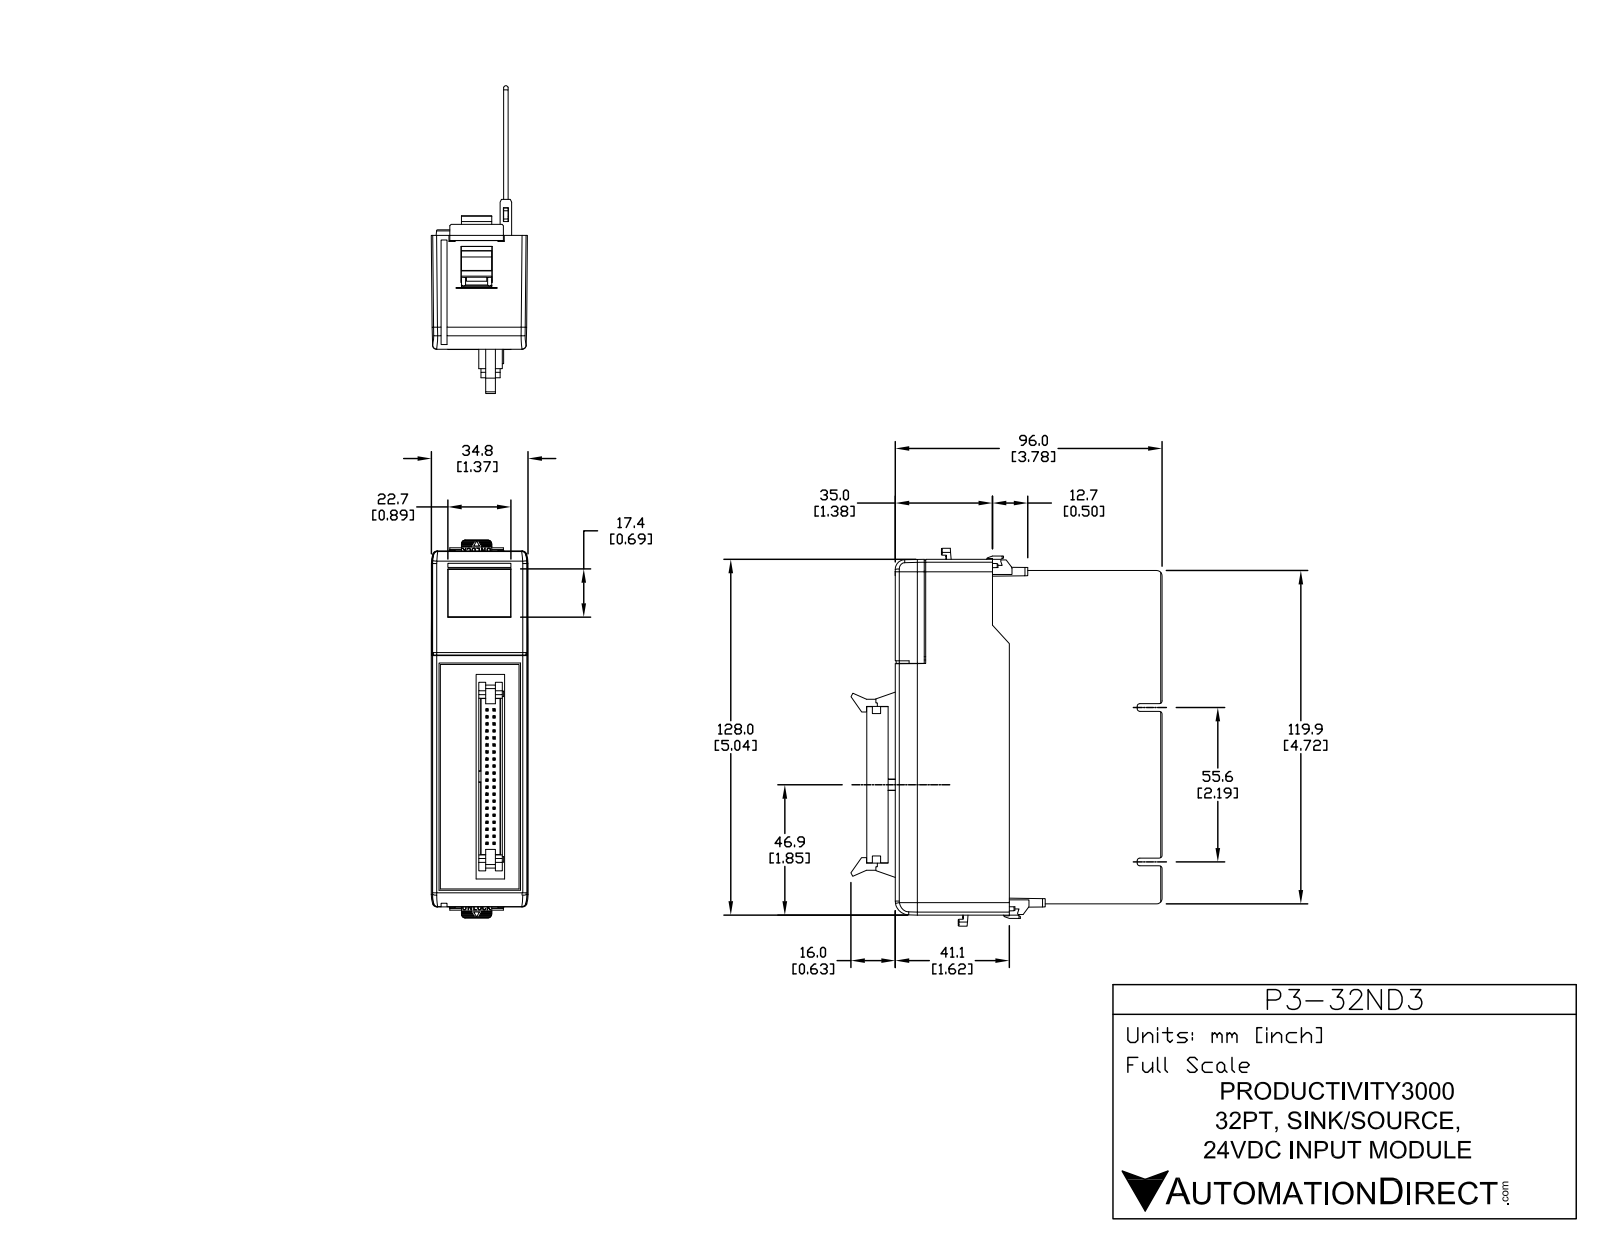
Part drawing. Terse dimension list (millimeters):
name: P3-32ND3
written by: SolidWorks 2009 (CONFIG_CONTROL_DESIGN)
unit: mm
bodies: 1 solid, 1418 faces (1334 planar, 54 cylindrical, 30 other)
size: 136.08 × 111.89 × 34.8
volume: 190 469 mm³; area: 44 248 mm²
rounds: 16× R1, 10× R0.3, 6× R1.5, 2× R0.1, 2× R0.5, 2× R1.15, 2× R1.2, 2× R2
face distances: 1.6, 41.23, 1.3, 2.9, 6.1, 35.13, 8.2, 7.7, 6.9, 9.8
